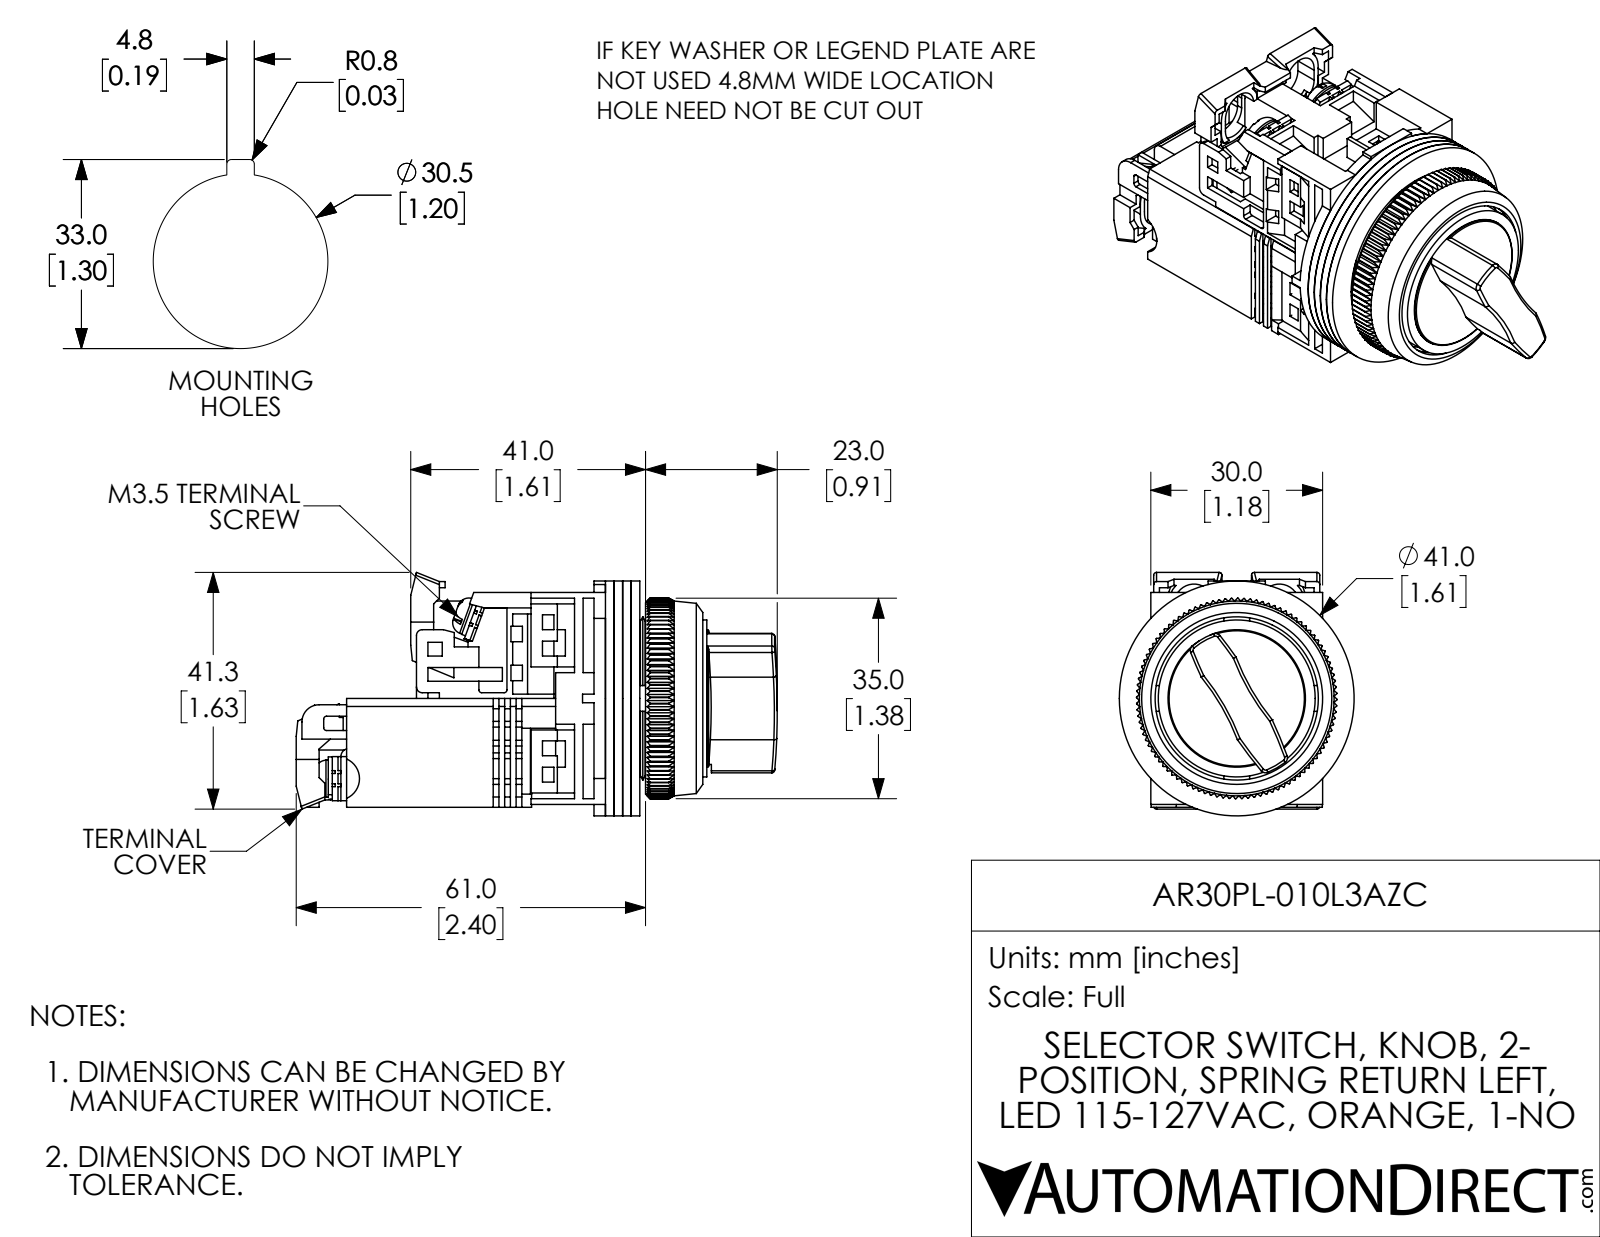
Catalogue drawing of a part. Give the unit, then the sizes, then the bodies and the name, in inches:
Units: inches
Overall size (bounding box): 3.307 × 1.673 × 1.614
Round holes (diameter × count): ⌀0.138 ×6, ⌀0.142 ×4, ⌀0.118 ×3, ⌀0.472 ×1, ⌀0.709 ×1, ⌀0.768 ×1, ⌀0.827 ×1, ⌀1.122 ×1, ⌀1.181 ×1, ⌀1.252 ×1
Round bosses / shafts (diameter × count): ⌀0.26 ×4, ⌀0.138 ×2, ⌀0.063 ×2, ⌀1.614 ×1, ⌀1.15 ×1, ⌀1.079 ×1, ⌀0.945 ×1, ⌀0.886 ×1
Partial cylindrical surfaces — rounded edges, fillets, slot ends (radius × count): R0.059 ×17, R0.02 ×13, R0.039 ×6, R0.138 ×4, R0.177 ×4, R0.118 ×2, R1.575 ×2, R2.953 ×2
Main face-to-face distances: 0.059, 0.118, 0.177, 0.079, 0.039, 0.748, 0.787, 0.197, 0.256, 1.417
Hole centre spacings: 0.579, 0.297, 0.624, 0.02, 0.302, 0.583, 0.583, 0.606
Volume: 3.001 in³ · Surface area: 63.38 in²
Bodies: 27 solids, 2357 faces (1706 planar, 321 cylindrical, 330 other)
Part name (STEP PRODUCT): AR30PL-010L3AZC
STEP written by: SolidWorks 2017 (AUTOMOTIVE_DESIGN)
